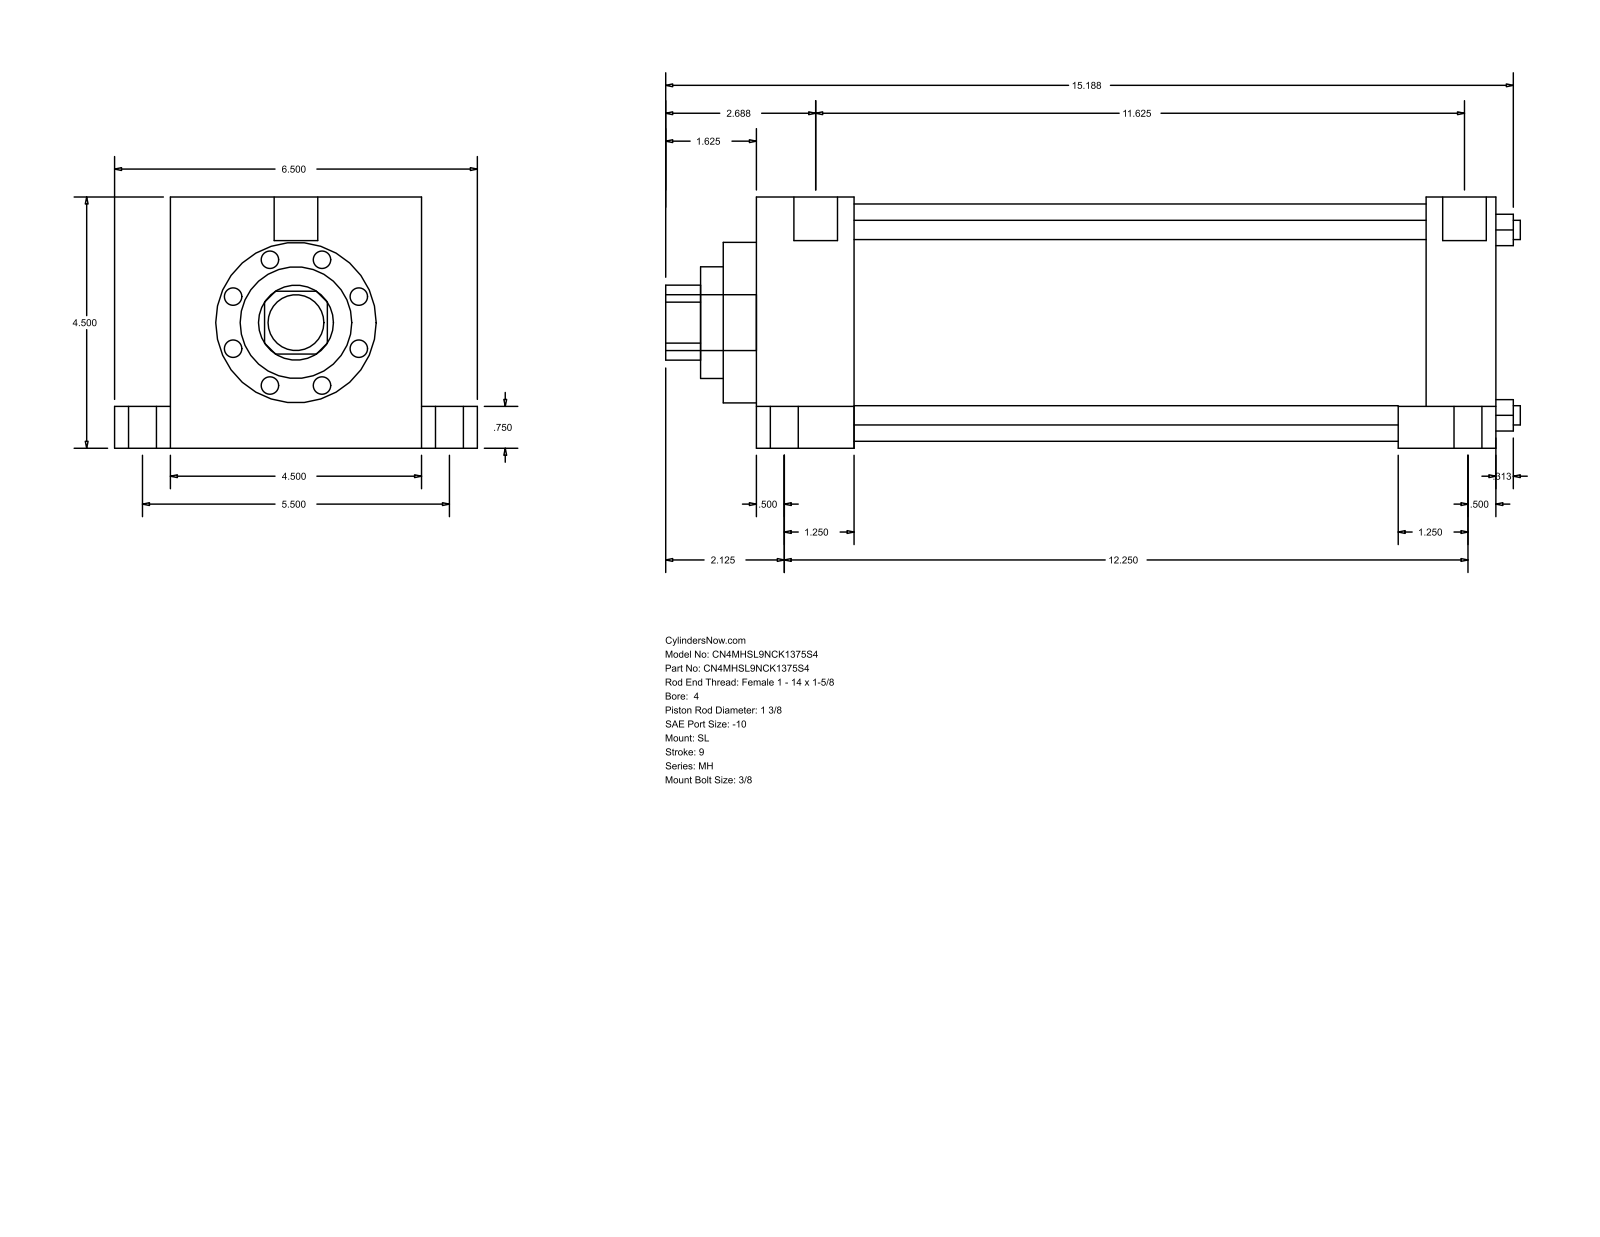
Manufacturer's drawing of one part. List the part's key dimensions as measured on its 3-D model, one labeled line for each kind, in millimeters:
Part name (STEP PRODUCT): MH_SL__0400_1.375
STEP written by: GSSL Pune (CONFIG_CONTROL_DESIGN)
Units: millimetres
Bodies: 0 solids, 110 faces (77 planar, 33 cylindrical, 0 other)
Overall size (bounding box): 388.94 × 165.1 × 114.3
Round holes (diameter × count): ⌀8.76 ×4, ⌀34.92 ×1, ⌀50.8 ×1, ⌀73.03 ×1, ⌀107.95 ×1
Round bosses / shafts (diameter × count): ⌀19.05 ×4, ⌀12.7 ×4, ⌀8.73 ×4, ⌀19.84 ×2, ⌀25.4 ×1
Partial cylindrical surfaces — rounded edges, fillets, slot ends (radius × count): R17.06 ×1
Main face-to-face distances: 114.3, 336.55, 44.45, 292.1, 304.8, 260.35, 31.75, 25.4, 139.7, 19.05
Hole centre spacings: 59.62, 84.32, 119.25
